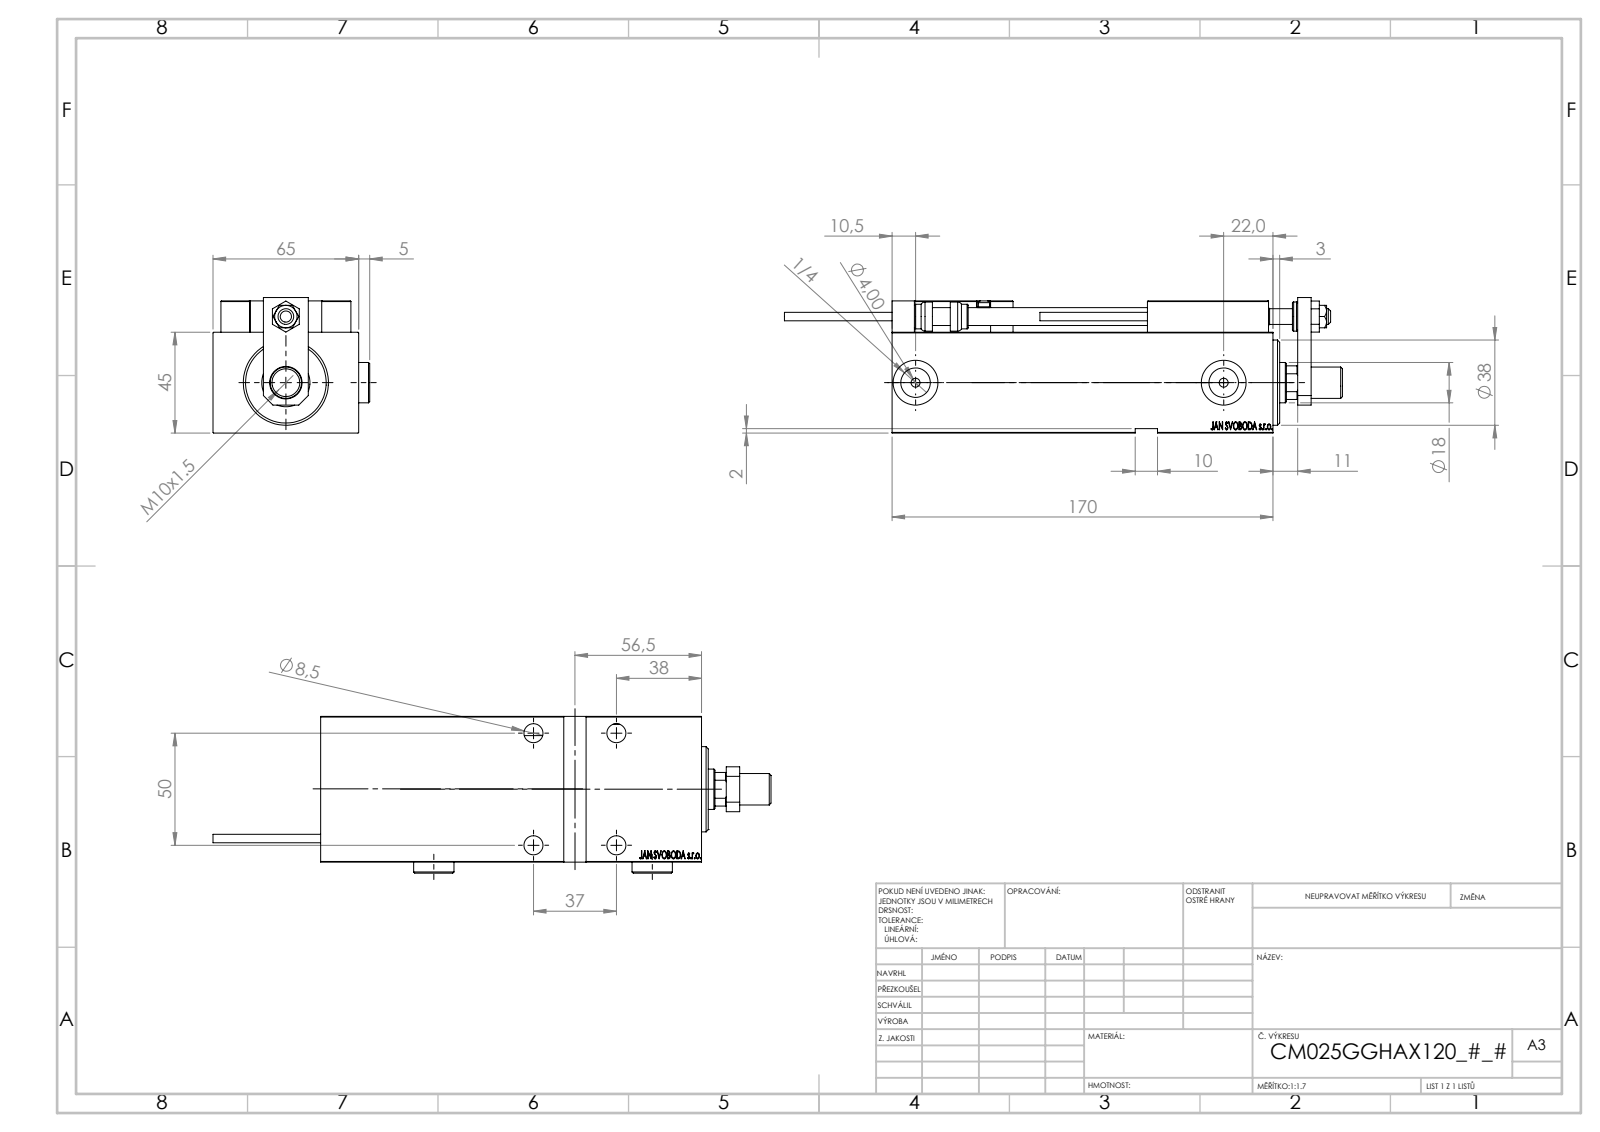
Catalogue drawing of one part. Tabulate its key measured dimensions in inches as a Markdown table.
| quantity | value |
| --- | --- |
| part name | ZARAZKA; V450CM_G_VCP; TYC_L79; NUT_D10 (+8 more) |
| STEP written by | SolidWorks 2019 (CONFIG_CONTROL_DESIGN) |
| units | inches |
| bodies | 27 solids, 1347 faces (604 planar, 192 cylindrical, 551 other) |
| overall size | 9.803 × 2.752 × 2.382 |
| volume | 31.06 in³ |
| surface area | 166.4 in² |
| round holes (diameter × count) | 0.157 × 6, 0.315 × 5, 0.335 × 5, 0.126 × 4, 0.531 × 4, 0.197 × 2, 0.518 × 2, 0.787 × 2, 0.276 × 1, 0.571 × 1, 0.709 × 1, 0.846 × 1 |
| round bosses / shafts (diameter × count) | 0.709 × 2, 0.197 × 2, 0.15 × 2, 1.496 × 1, 0.551 × 1, 0.512 × 1, 0.472 × 1, 0.433 × 1 |
| partial cylindrical surfaces (radius × count) | 0.012 × 30, 0.118 × 2, 0.335 × 1 |
| main face-to-face distances | 1.772, 2.559, 0.551, 0.236, 2.323, 6.693, 7.126, 0.197, 0.512, 0.433 |
| hole center spacings | 0.448, 0.787, 1.165, 1.169, 1.356, 1.42, 1.457, 1.661 |
